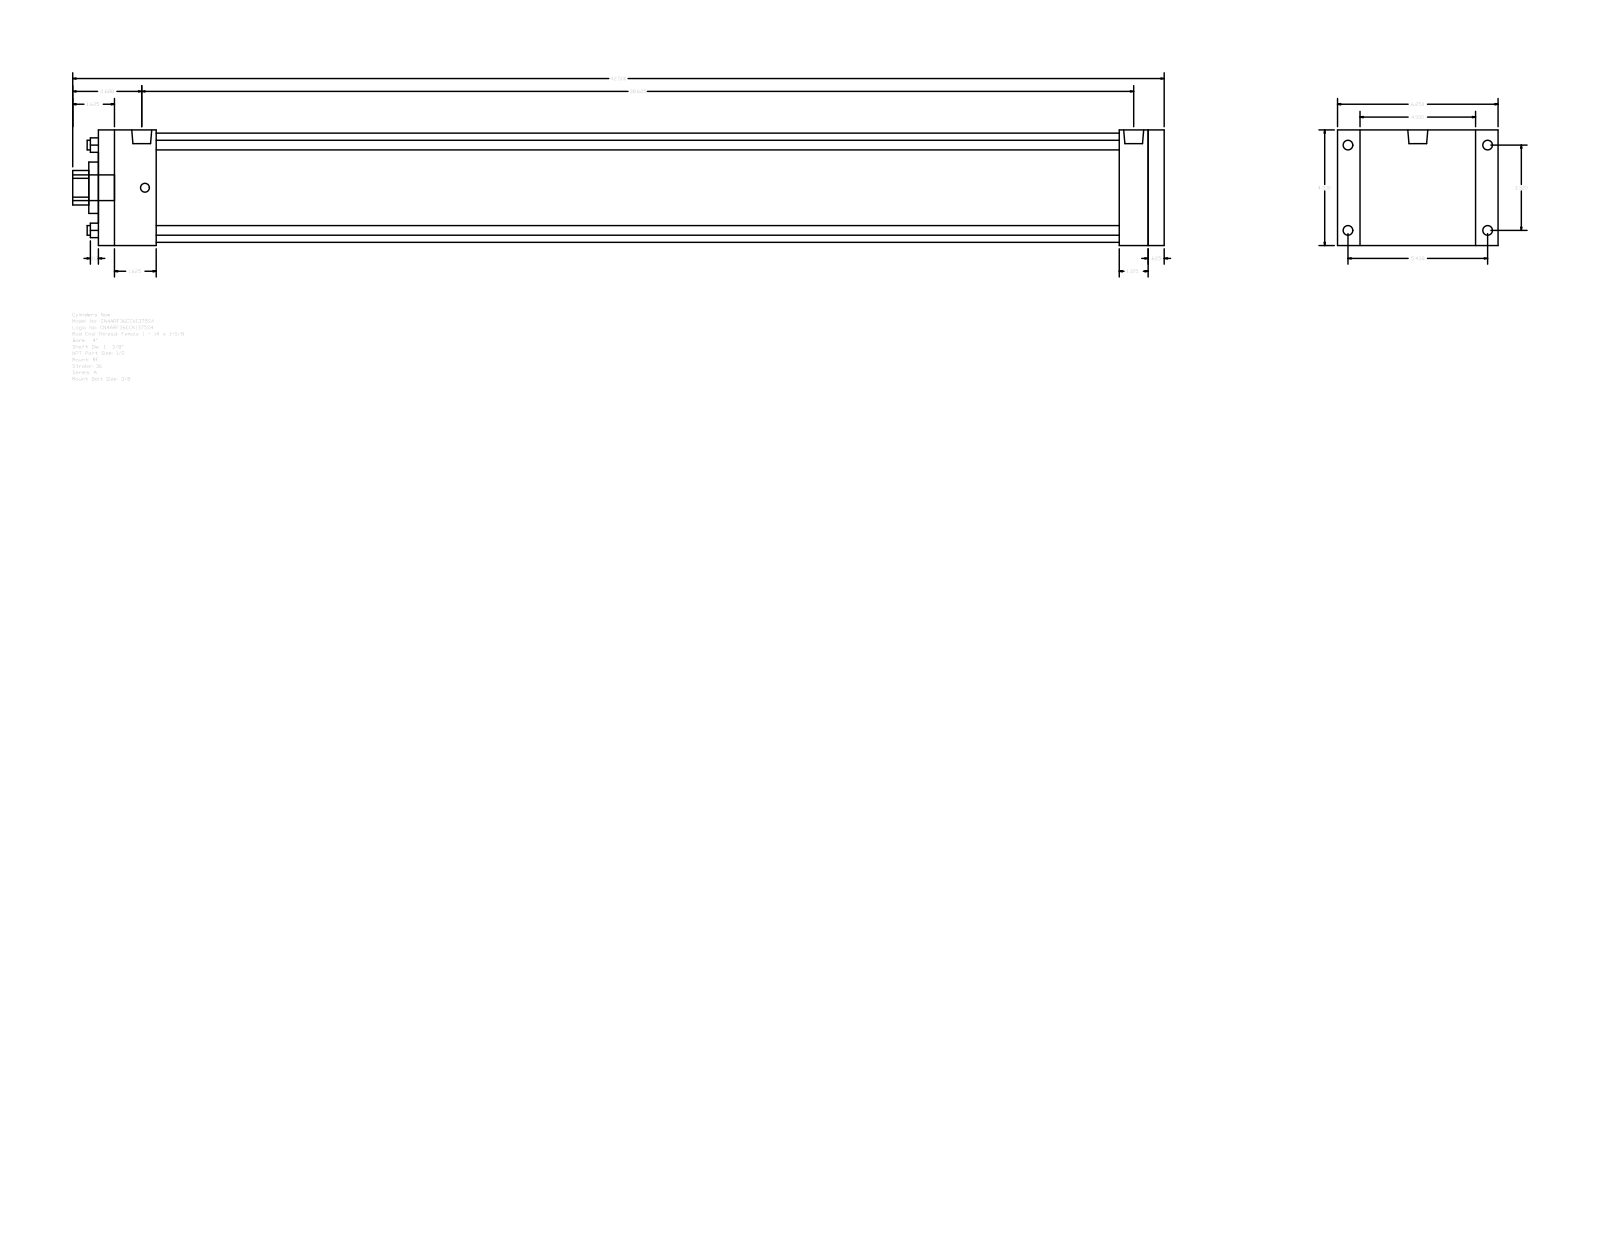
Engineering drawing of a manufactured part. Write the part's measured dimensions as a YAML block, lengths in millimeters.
part_name: "A_RF__0400_1.375"
step_written_by: "GSSL Pune (CONFIG_CONTROL_DESIGN)"
units: millimeters
bodies: {solids: 0, faces: 92, planar: 64, cylindrical: 28, other: 0}
overall_size: [1079.5, 158.75, 114.3]
round_holes:
  - {diameter: 9.53, count: 4}
  - {diameter: 34.92, count: 1}
  - {diameter: 50.8, count: 1}
  - {diameter: 107.95, count: 1}
round_bosses_or_shafts:
  - {diameter: 9.53, count: 4}
  - {diameter: 8.73, count: 4}
  - {diameter: 19.77, count: 2}
  - {diameter: 25.4, count: 1}
partial_cylinders:
  - {radius: 17.06, count: 1}
face_to_face_distances: [114.3, 1054.1, 15.88, 1038.22, 28.57, 22.23, 136.53, 1009.65, 44.45, 57.15]
hole_center_spacings: [59.62, 84.32, 119.25]
